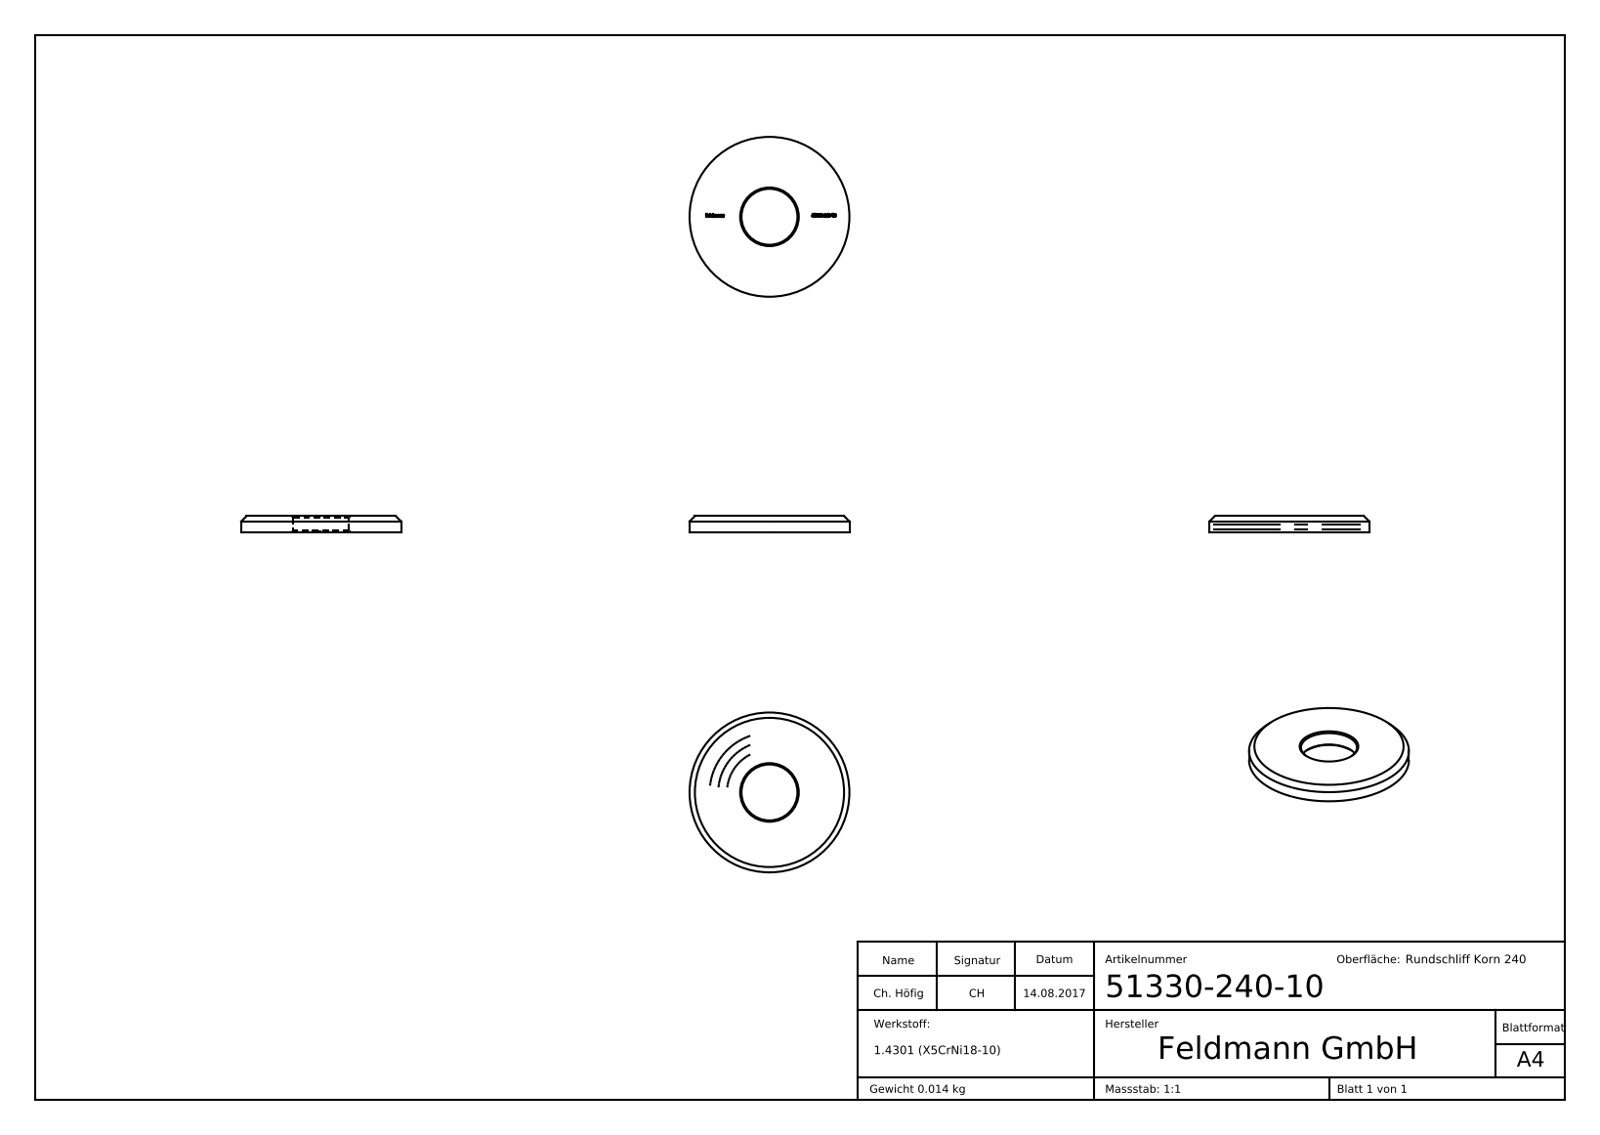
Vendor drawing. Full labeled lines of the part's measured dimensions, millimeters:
Part name (STEP PRODUCT): 51330-240-10
STEP written by: SolidWorks 2018 (CONFIG_CONTROL_DESIGN)
Units: millimetres
Bodies: 1 solid, 261 faces (134 planar, 4 cylindrical, 123 other)
Overall size (bounding box): 30 × 30 × 3
Volume: 1 813 mm³ · Surface area: 1 560 mm²
Round holes (diameter × count): ⌀10.5 ×1
Round bosses / shafts (diameter × count): ⌀30 ×1
Main face-to-face distances: 3, 2.9, 1.19, 19.72, 23.06, 3.34, 0.35, 0.53, 22.09, 2.37
